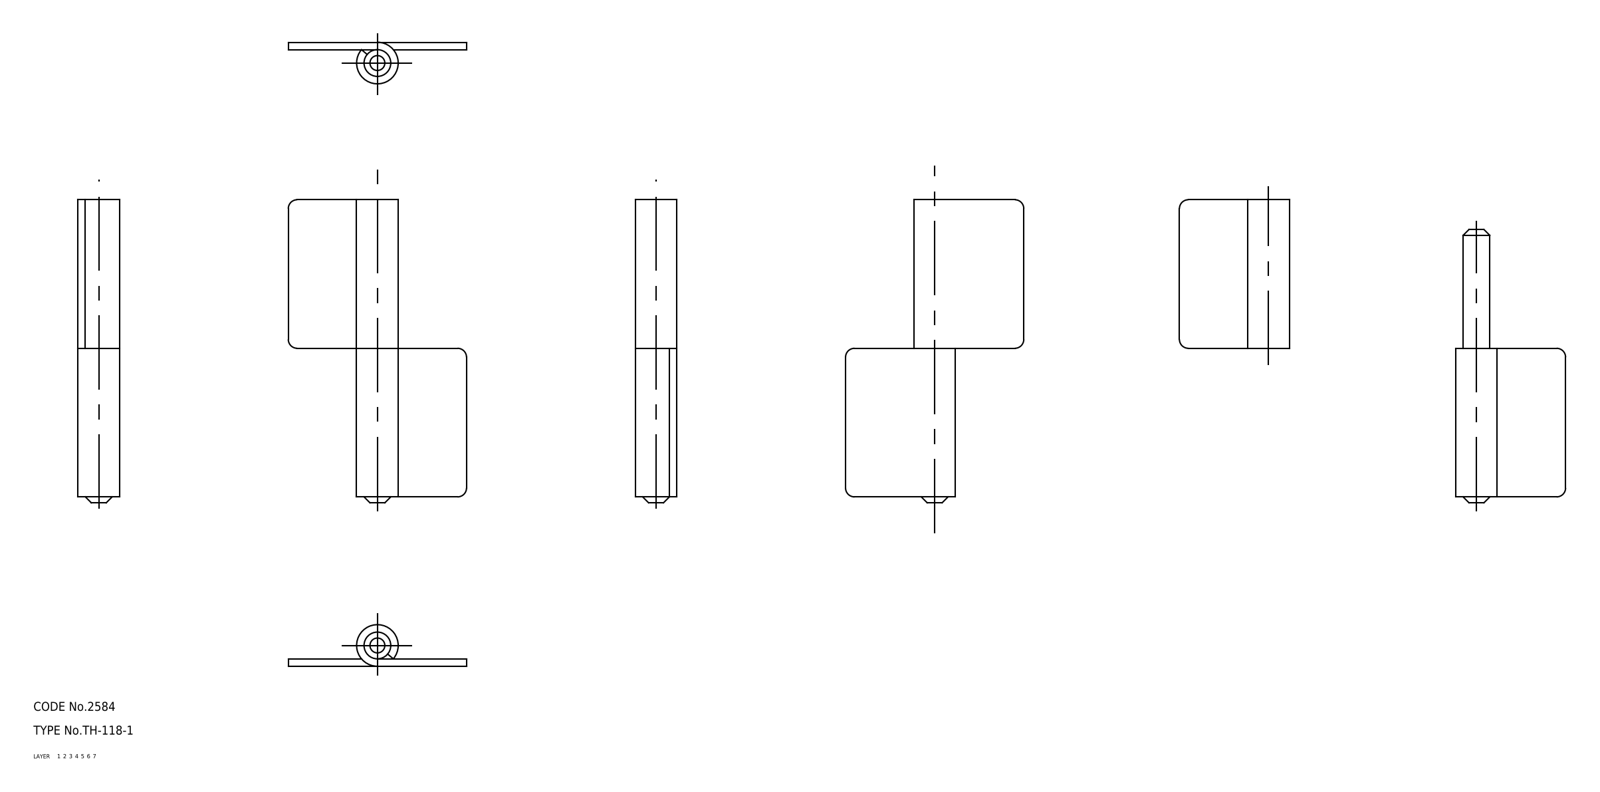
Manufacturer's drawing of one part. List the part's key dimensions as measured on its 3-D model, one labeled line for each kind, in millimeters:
Part name (STEP PRODUCT): shaft; hinge piece_B; hinge piece_A; TH_118_1_32631_36
STEP written by: CADfix (AUTOMOTIVE_DESIGN)
Units: millimetres
Bodies: 3 solids, 28 faces (0 planar, 0 cylindrical, 28 other)
Overall size (bounding box): 102 × 60 × 14
Volume: 21 011 mm³ · Surface area: 15 948 mm²
